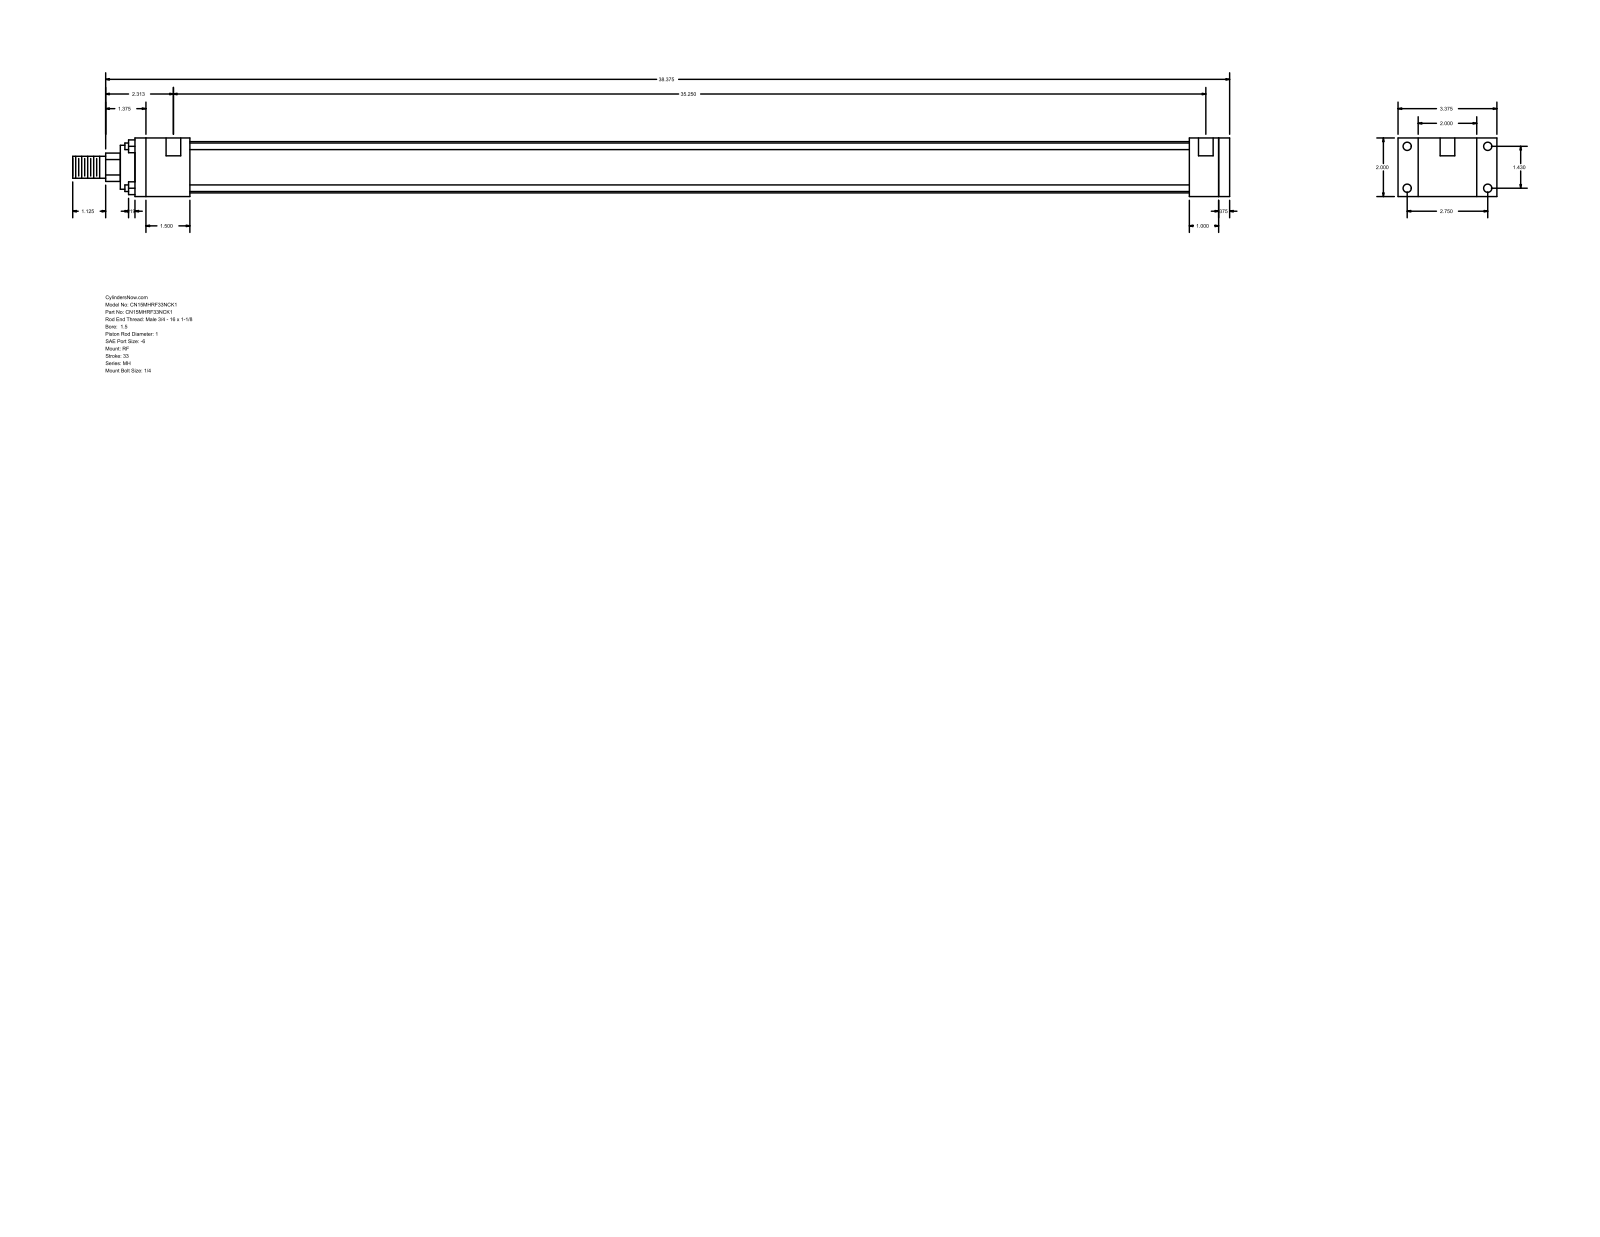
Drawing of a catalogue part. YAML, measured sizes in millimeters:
part_name: "MH_RF__0150_1"
step_written_by: "GSSL Pune (CONFIG_CONTROL_DESIGN)"
units: millimeters
bodies: {solids: 0, faces: 92, planar: 64, cylindrical: 28, other: 0}
overall_size: [1003.3, 85.72, 50.8]
round_holes:
  - {diameter: 5.56, count: 4}
  - {diameter: 7.14, count: 4}
  - {diameter: 12.7, count: 2}
round_bosses_or_shafts:
  - {diameter: 5.71, count: 4}
  - {diameter: 44.45, count: 1}
  - {diameter: 38.1, count: 1}
  - {diameter: 25.4, count: 1}
  - {diameter: 19.05, count: 1}
partial_cylinders:
  - {radius: 12.29, count: 1}
face_to_face_distances: [50.8, 9.53, 939.8, 25.4, 949.33, 17.46, 68.26, 914.4, 34.93, 47.63]
hole_center_spacings: [36.32, 69.84, 78.72, 898.53, 3.18, 895.35]
